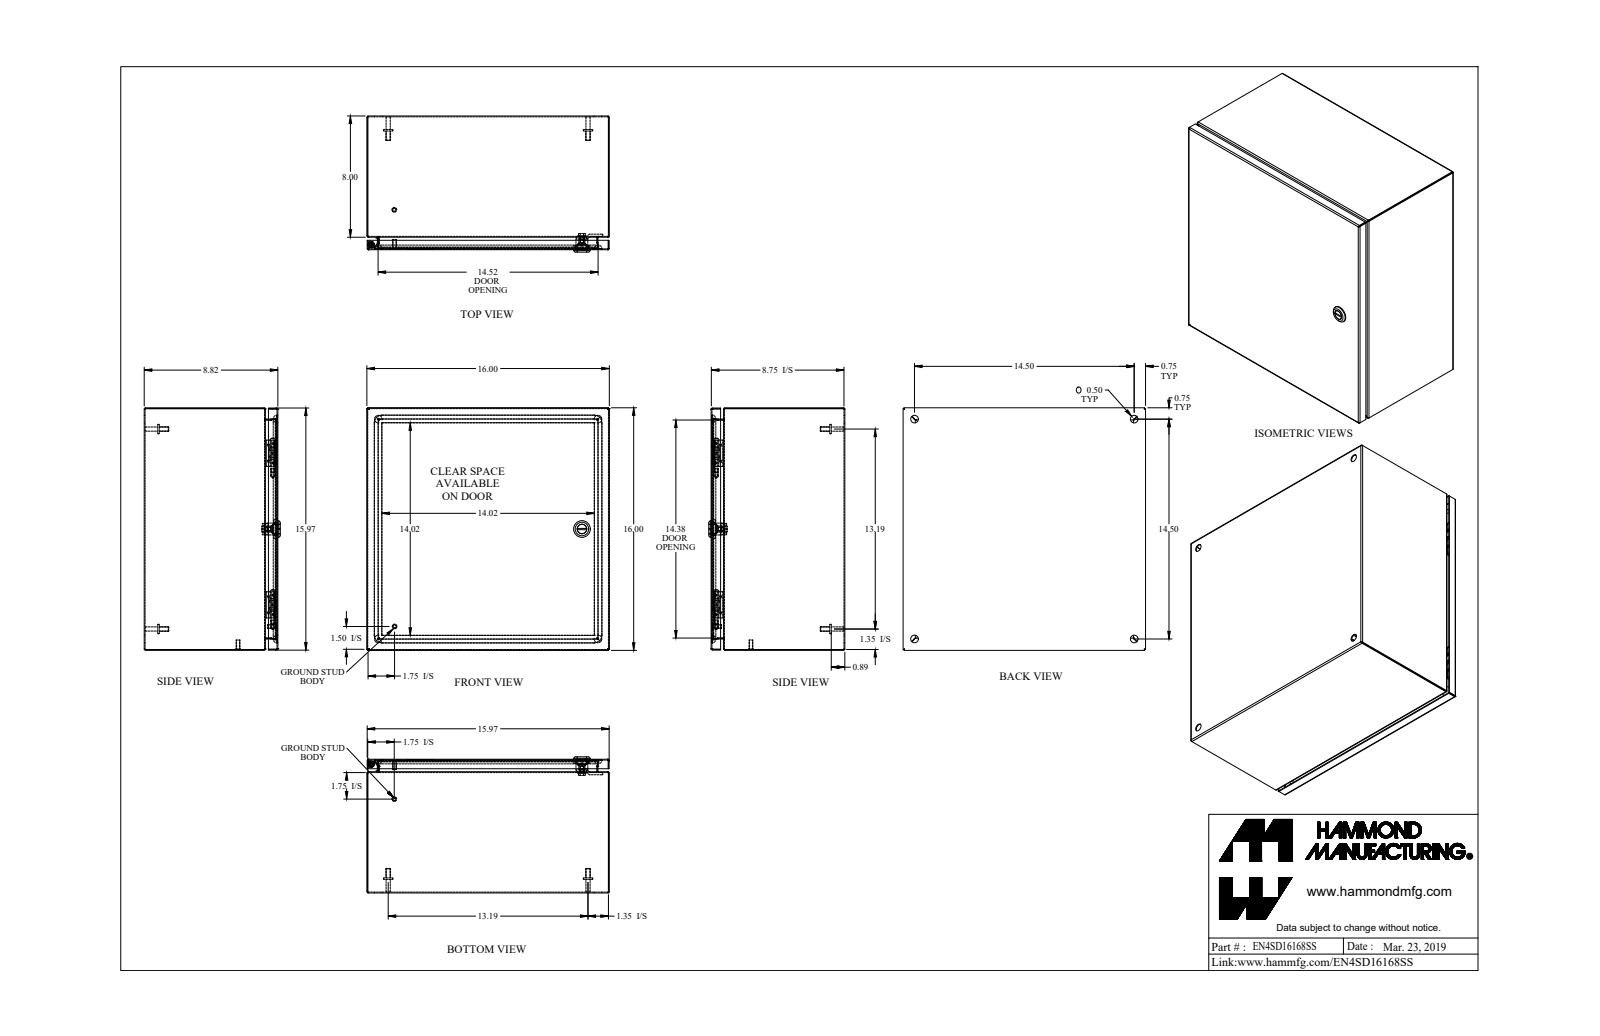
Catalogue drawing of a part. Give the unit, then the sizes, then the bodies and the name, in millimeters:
Units: millimetres
Overall size (bounding box): 406.4 × 406.4 × 228.1
Round holes (diameter × count): ⌀12.7 ×5, ⌀4.4 ×1, ⌀5 ×1, ⌀6.1 ×1, ⌀6.1 ×1, ⌀9.8 ×1, ⌀16 ×1, ⌀19.5 ×1
Round bosses / shafts (diameter × count): ⌀8 ×6, ⌀15.9 ×4, ⌀7 ×4, ⌀6.4 ×2, ⌀27.9 ×1, ⌀19.9 ×1, ⌀15.9 ×1, ⌀13.3 ×1
Partial cylindrical surfaces — rounded edges, fillets, slot ends (radius × count): R0.7 ×21, R2.2 ×21, R4.8 ×12, R0.2 ×4, R1.6 ×4, R6.4 ×4, R12.7 ×4, R3.2 ×2
Main face-to-face distances: 1.4, 222.6, 405, 403.5, 221.2, 224.1, 406.4, 20.9, 201.8, 19
Hole centre spacings: 368.3, 186.1, 387.9, 520.9
Volume: 1 178 000 mm³ · Surface area: 1 576 000 mm²
Bodies: 22 solids, 657 faces (303 planar, 212 cylindrical, 142 other)
Part name (STEP PRODUCT): EN4SD16168SS_Default
STEP written by: SolidWorks 2019 (CONFIG_CONTROL_DESIGN)
